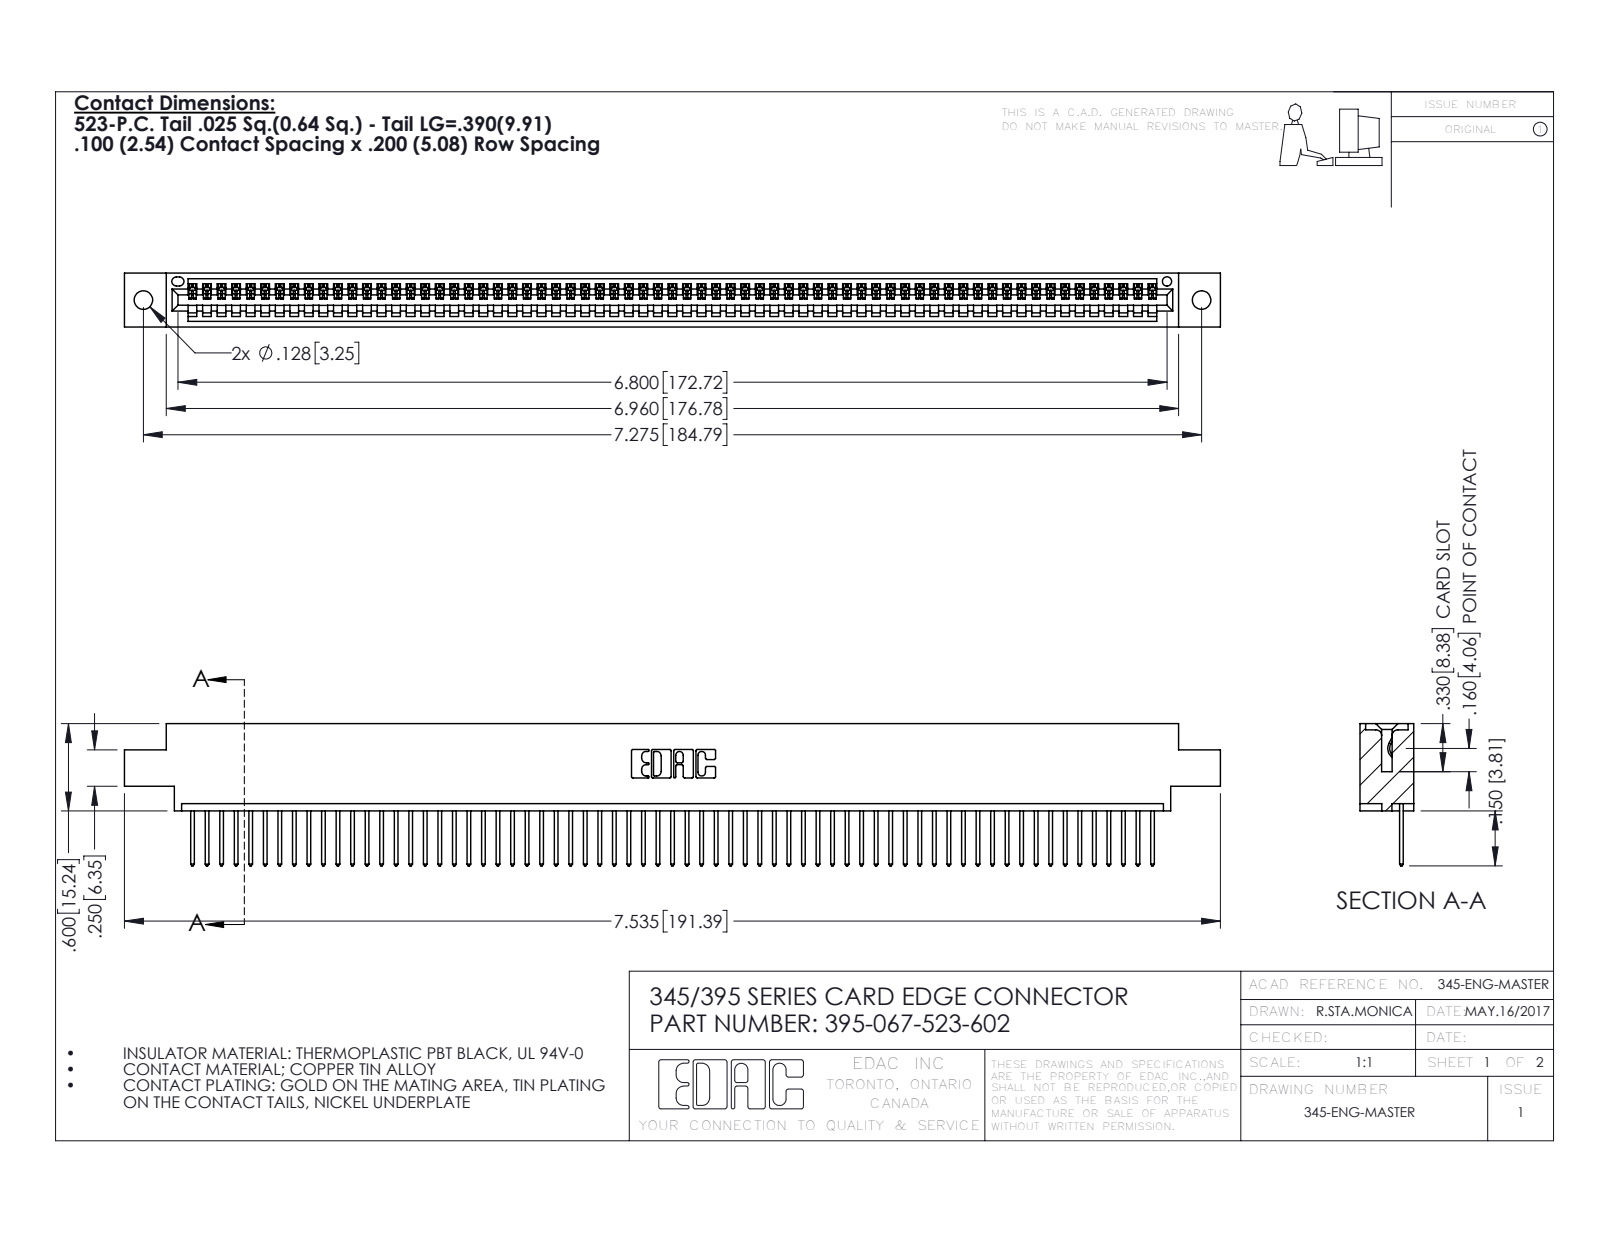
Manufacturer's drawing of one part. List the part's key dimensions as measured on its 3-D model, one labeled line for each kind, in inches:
Part name (STEP PRODUCT): 395-067-523-602; 345-292-001_345-293-123; 345 Part_0.170 Offset - 0.128 Dia
STEP written by: SolidWorks 2016 (CONFIG_CONTROL_DESIGN)
Units: inches
Bodies: 68 solids, 4016 faces (2764 planar, 1252 cylindrical, 0 other)
Overall size (bounding box): 7.535 × 0.977 × 0.37
Volume: 1.111 in³ · Surface area: 37.92 in²
Round holes (diameter × count): ⌀0.128 ×2, ⌀0.064 ×1
Partial cylindrical surfaces — rounded edges, fillets, slot ends (radius × count): R0.006 ×134, R0.01 ×134, R0.01 ×22, R0.007 ×6, R0.031 ×6, R0.026 ×3, R0.031 ×2, R0.04 ×2
Main face-to-face distances: 0.298, 0.072, 0.37, 0.098, 0.272, 0.025, 0.2, 0.225, 0.175, 0.149
Hole centre spacings: 0.27, 7.039, 7.275
